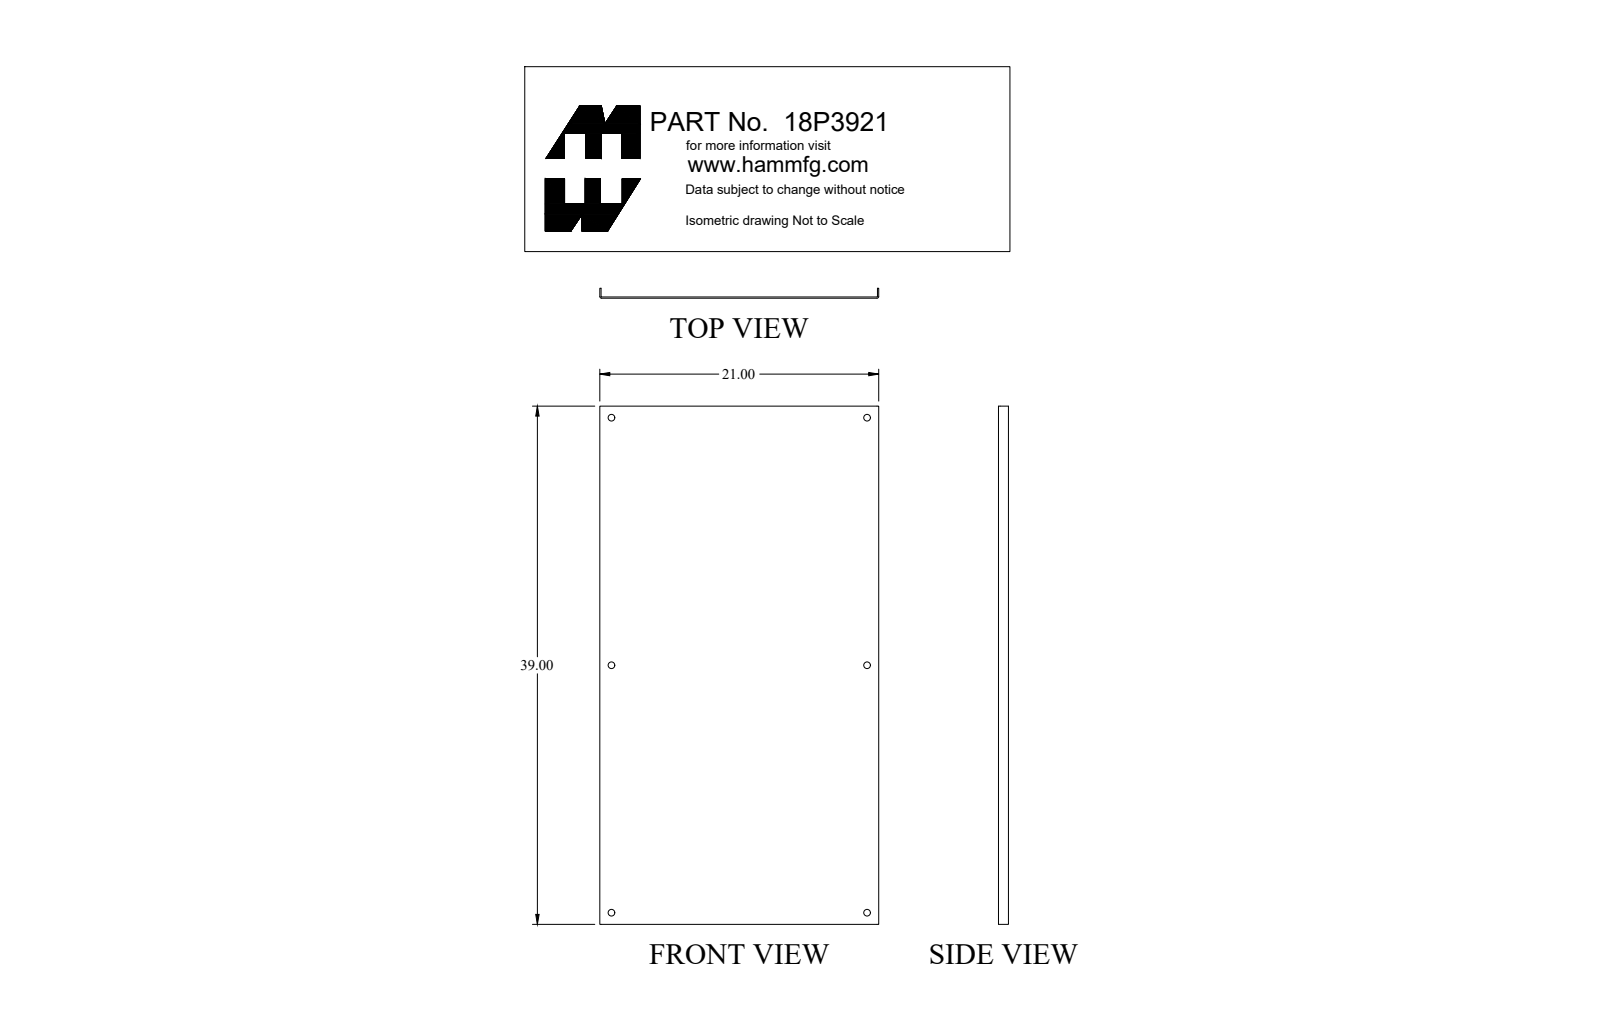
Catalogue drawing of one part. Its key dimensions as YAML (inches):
part_name: "18P3921_Default"
step_written_by: "SolidWorks 2018 (CONFIG_CONTROL_DESIGN)"
units: inches
bodies: {solids: 1, faces: 26, planar: 10, cylindrical: 16, other: 0}
overall_size: [39, 21, 0.75]
volume: 82.3
surface_area: 1745
round_holes:
  - {diameter: 0.5, count: 6}
partial_cylinders:
  - {radius: 0.03, count: 2}
  - {radius: 0.125, count: 2}
face_to_face_distances: [0.095, 20.905, 20.81, 21, 0.75, 0.655, 39]
hole_center_spacings: [18.625, 26.785, 19.25, 37.25, 41.93]
